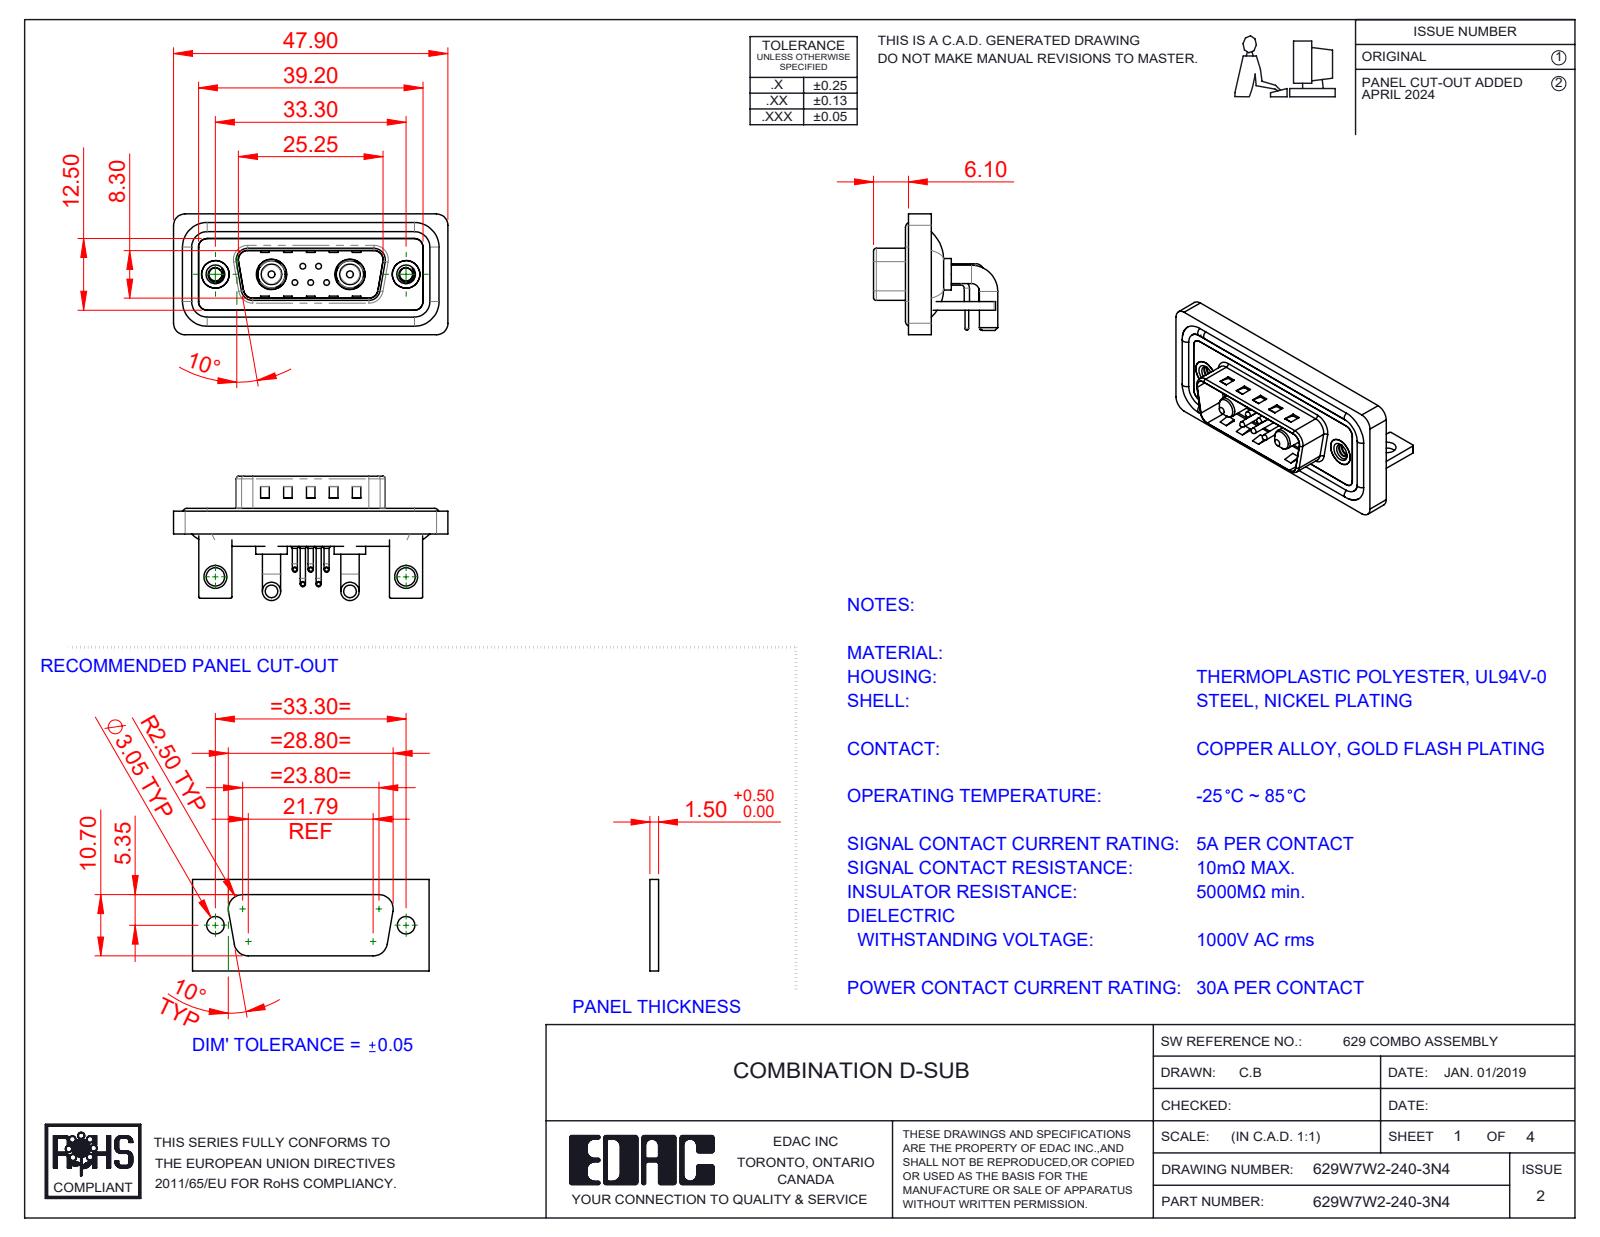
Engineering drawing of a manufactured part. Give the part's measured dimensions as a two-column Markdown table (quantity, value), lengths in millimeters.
| quantity | value |
| --- | --- |
| part name | 629Combo Shell Front_15 Contacts; 629W7W2-140-3N4; 629Combo Waterproof Housing_15 Contacts; 629Combo Stabilizer Bracket (+6 more) |
| STEP written by | SolidWorks 2023 (CONFIG_CONTROL_DESIGN) |
| units | millimeters |
| bodies | 18 solids, 1123 faces (537 planar, 424 cylindrical, 162 other) |
| overall size | 47.9 × 21.7 × 21.1 |
| volume | 6 014 mm³ |
| surface area | 9 764 mm² |
| round holes (diameter × count) | 0.75 × 5, 1.6 × 5, 2 × 5, 2.26 × 2, 3.2 × 2, 4 × 2, 4.8 × 2, 4.85 × 2, 5 × 2, 5.3 × 2 |
| round bosses / shafts (diameter × count) | 0.9 × 10, 1.5 × 5, 1 × 5, 0.65 × 5, 3.2 × 4, 1.6 × 4, 5.5 × 2, 5.2 × 2 |
| partial cylindrical surfaces (radius × count) | 2 × 21, 1.5 × 18, 0.25 × 16, 0.5 × 9, 1.6 × 8, 1.01 × 5, 0.6 × 4, 0.65 × 4 |
| main face-to-face distances | 0.4, 1.5, 0.8, 2.9, 2.1, 1.1, 1.6, 1.2, 3.7, 4.5 |
| hole center spacings | 3.16, 2.77, 9.8, 23.5, 33.3, 4.31, 4.33, 5.03 |
